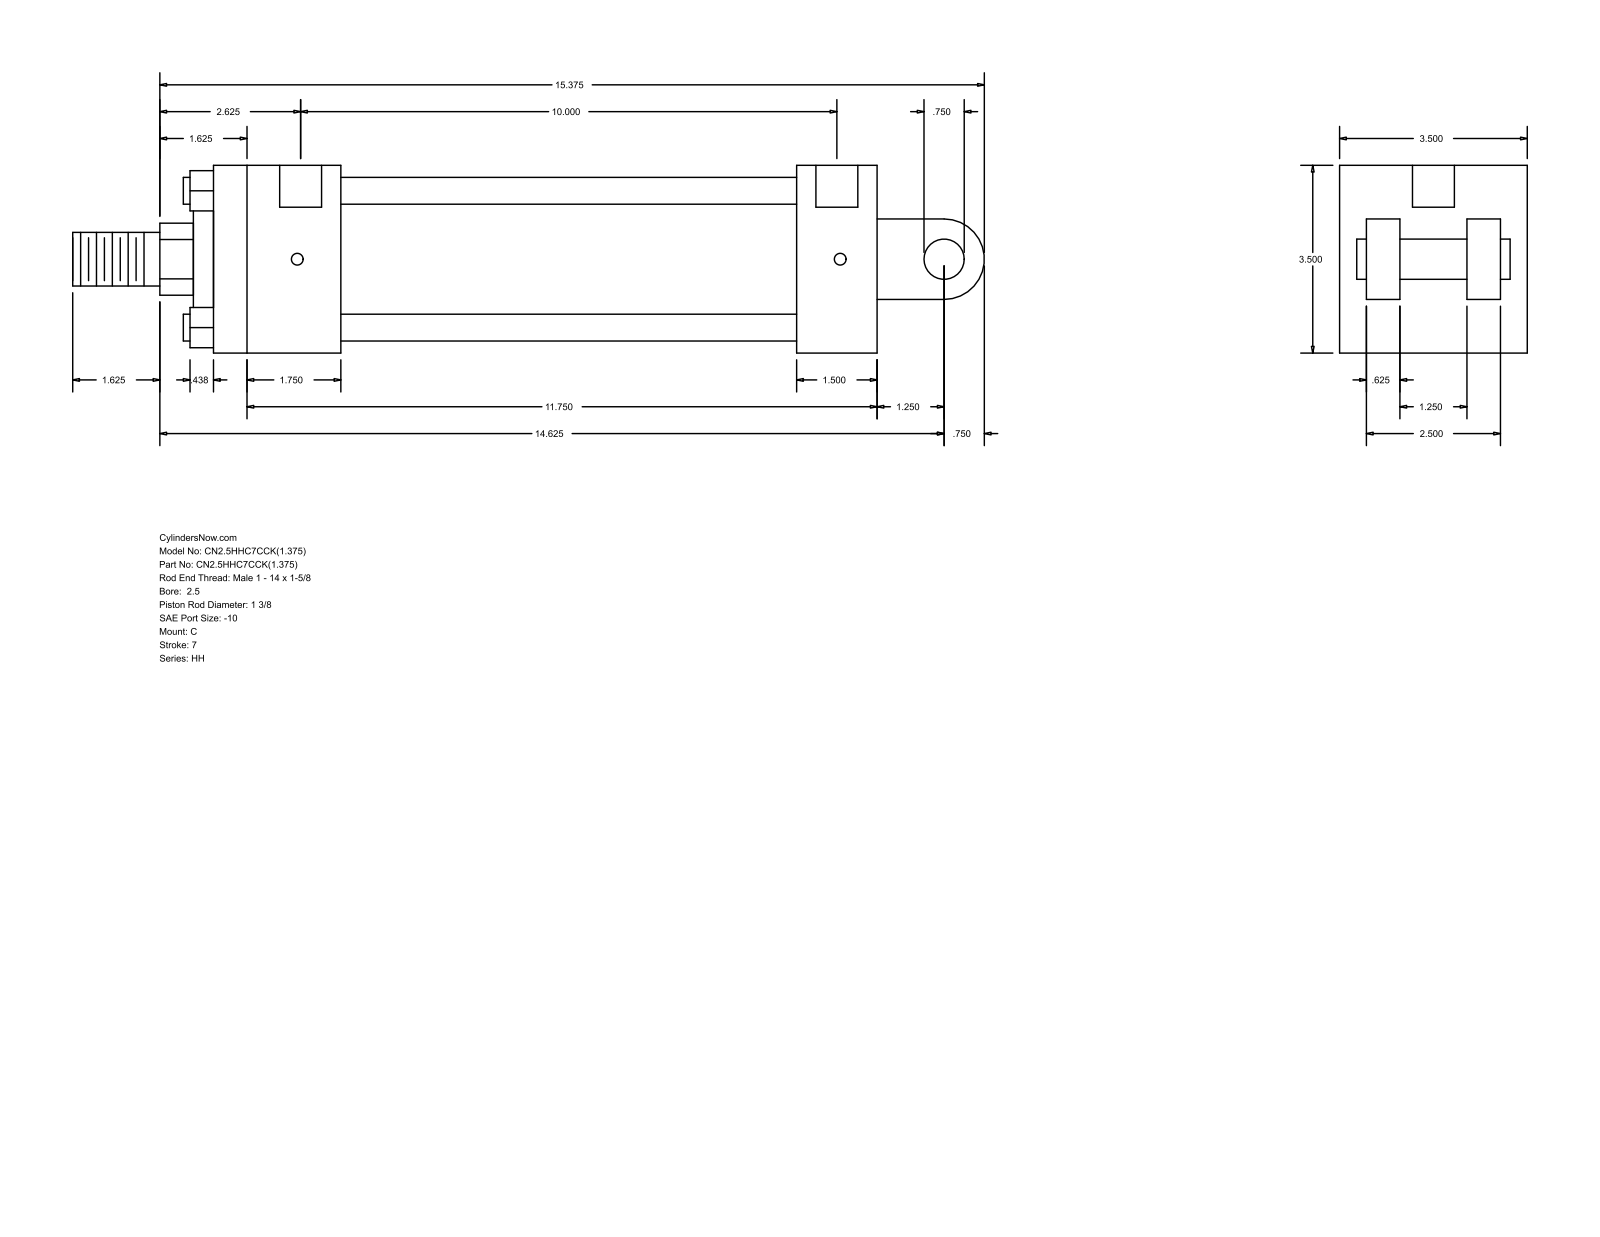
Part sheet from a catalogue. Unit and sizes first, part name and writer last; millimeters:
Units: millimetres
Overall size (bounding box): 431.8 × 88.9 × 88.9
Round holes (diameter × count): ⌀5.56 ×4, ⌀19.84 ×2
Round bosses / shafts (diameter × count): ⌀12.7 ×4, ⌀73.03 ×1, ⌀50.8 ×1, ⌀34.92 ×1, ⌀25.4 ×1, ⌀19.05 ×1
Partial cylindrical surfaces — rounded edges, fillets, slot ends (radius × count): R17.06 ×1, R19.05 ×1
Main face-to-face distances: 88.9, 314.33, 63.5, 12.7, 276.22, 38.11, 60.32, 215.9, 254.01, 76.2
Hole centre spacings: 1.58, 255.59, 257.17, 254.01
Bodies: 0 solids, 99 faces (70 planar, 29 cylindrical, 0 other)
Part name (STEP PRODUCT): HH_C__0250_1.375
STEP written by: GSSL Pune (CONFIG_CONTROL_DESIGN)
